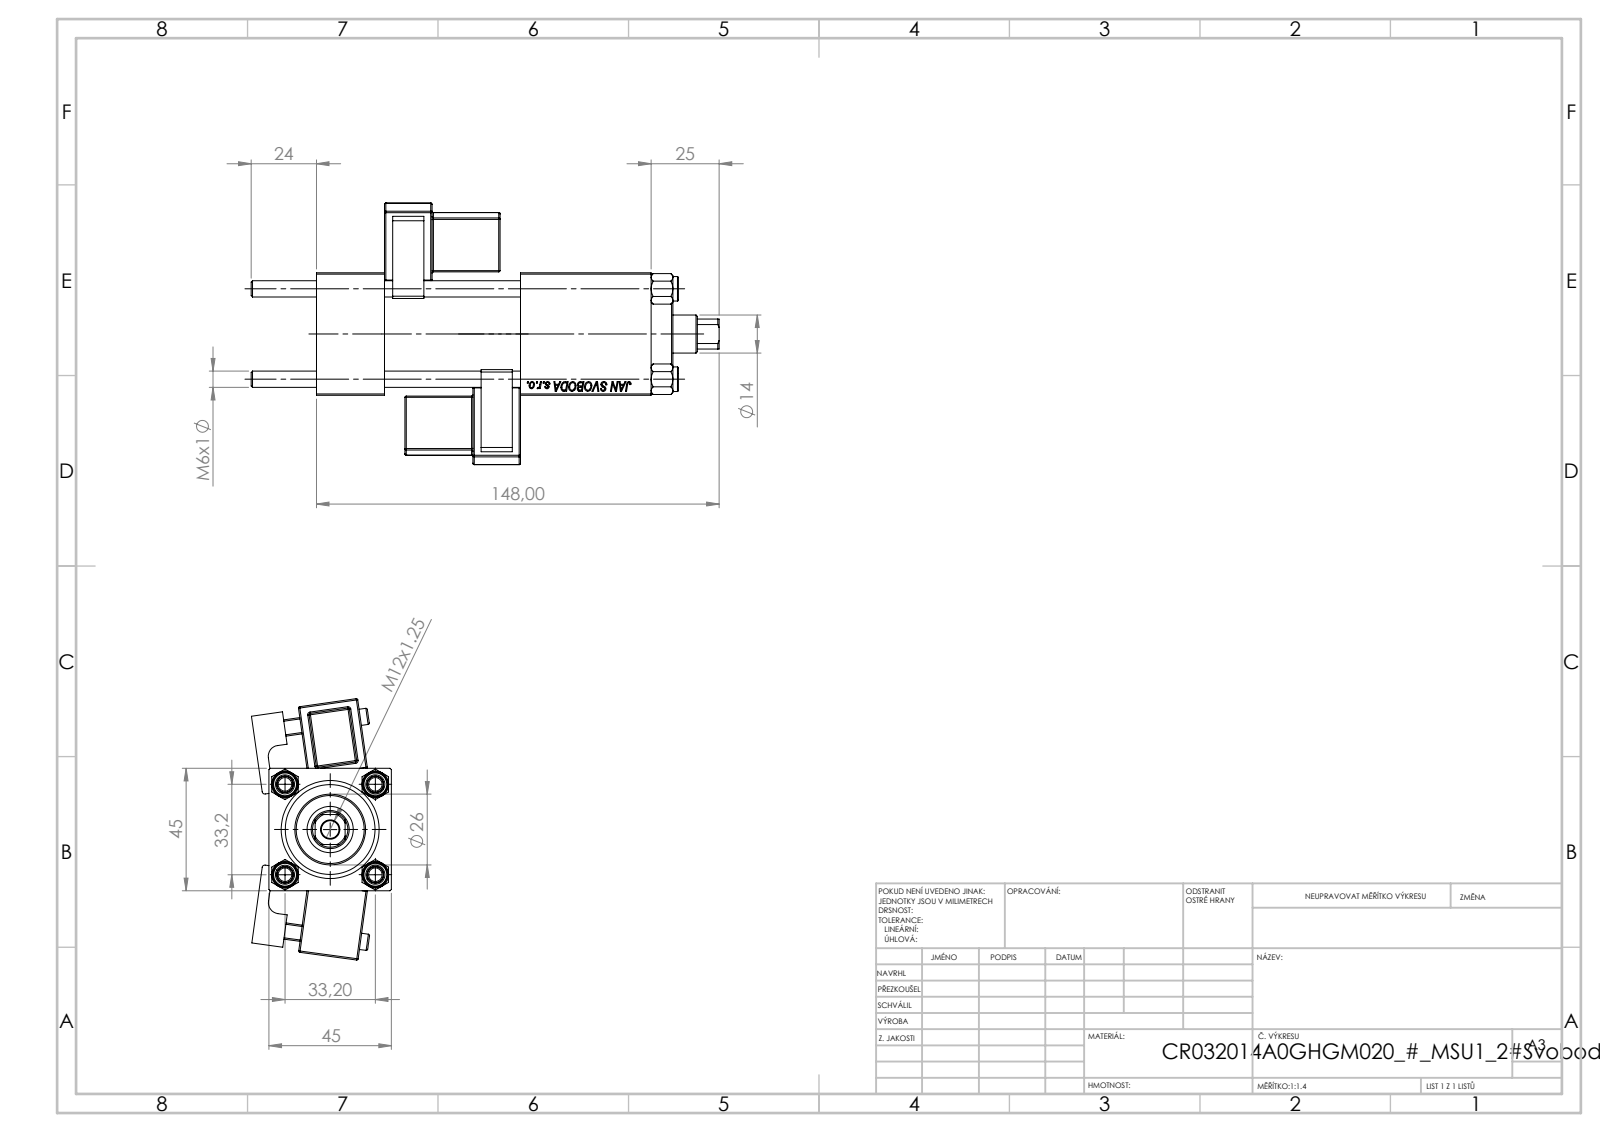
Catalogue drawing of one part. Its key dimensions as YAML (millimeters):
part_name: "NUT_M5; V215CR_BODY_A; V215_VC_A; CR025_012_A_0_G_A_G_M_020_+#_##_TYCINKA (+2 more)"
step_written_by: "SolidWorks 2019 (CONFIG_CONTROL_DESIGN)"
units: millimeters
bodies: {solids: 13, faces: 1291, planar: 581, cylindrical: 138, other: 572}
overall_size: [172, 96.03, 51.41]
volume: 238969
surface_area: 84824
round_holes:
  - {diameter: 6, count: 4}
  - {diameter: 7, count: 2}
  - {diameter: 13.16, count: 2}
  - {diameter: 20, count: 2}
  - {diameter: 6.5, count: 1}
  - {diameter: 14, count: 1}
  - {diameter: 17, count: 1}
  - {diameter: 24, count: 1}
  - {diameter: 32, count: 1}
  - {diameter: 33, count: 1}
round_bosses_or_shafts:
  - {diameter: 9, count: 4}
  - {diameter: 6, count: 2}
  - {diameter: 38, count: 1}
  - {diameter: 26, count: 1}
partial_cylinders:
  - {radius: 0.5, count: 48}
  - {radius: 1, count: 2}
  - {radius: 2.5, count: 2}
  - {radius: 4, count: 2}
  - {radius: 6.5, count: 1}
face_to_face_distances: [45, 25, 3, 50, 75, 98, 123, 15, 48, 32.5]
hole_center_spacings: [23.48, 33.2, 46.95, 75.5]
